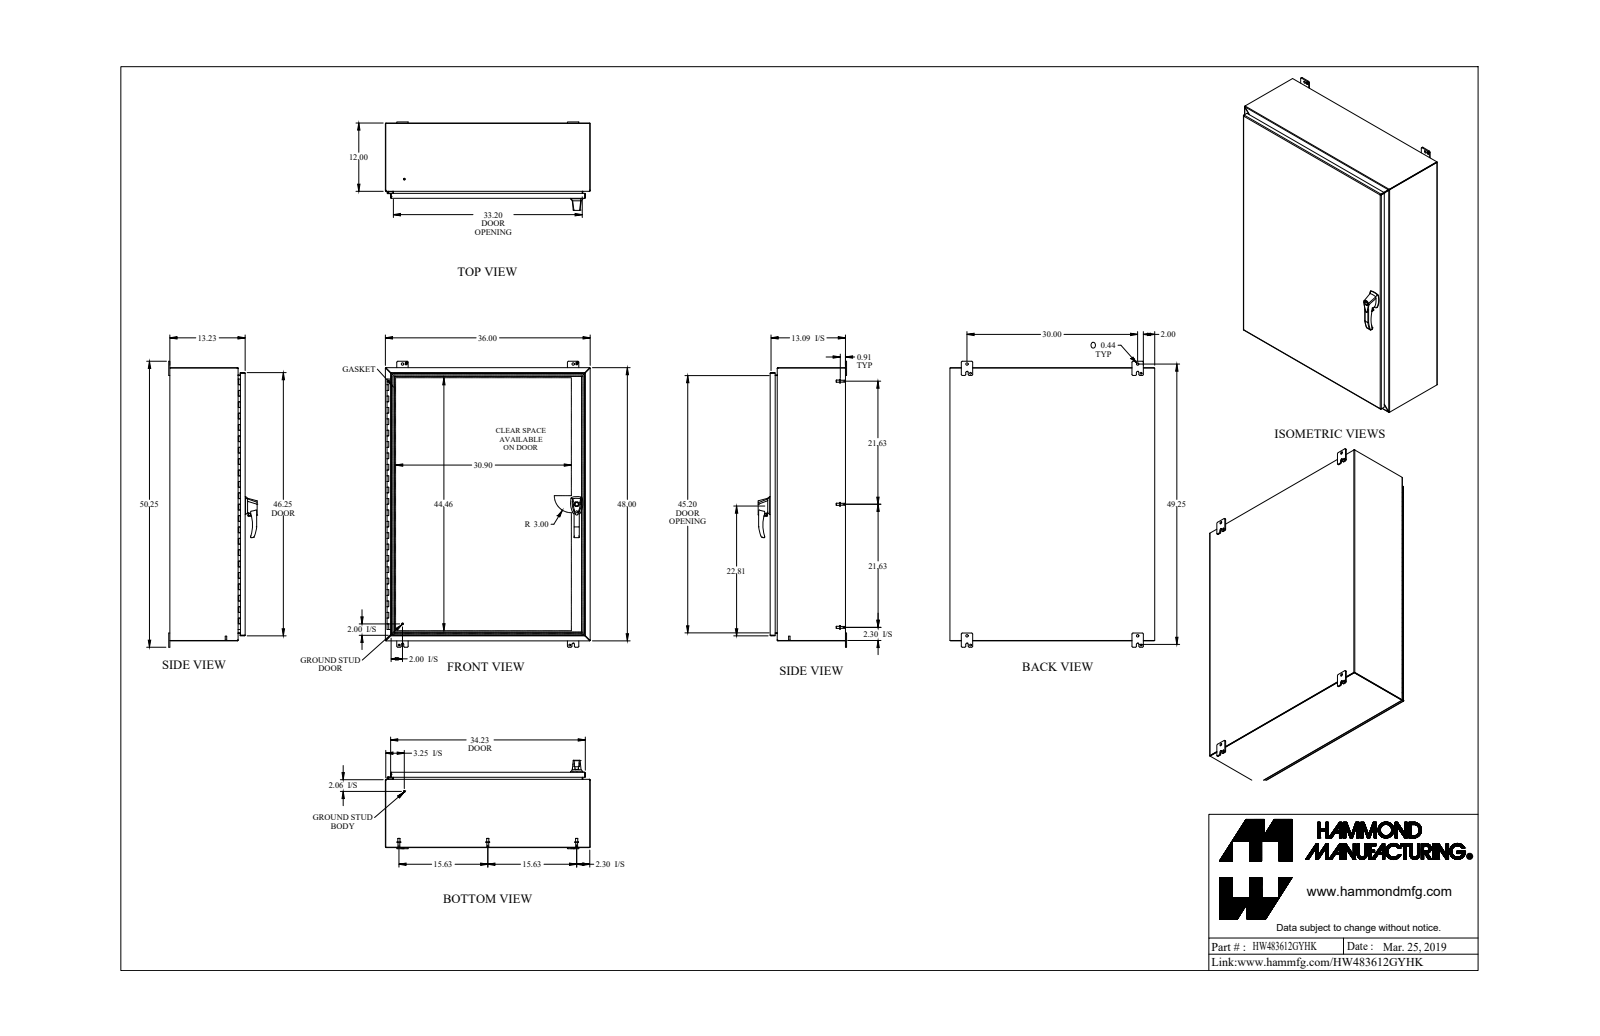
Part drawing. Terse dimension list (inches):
name: HW483612GYHK
written by: SolidWorks 2018 (AUTOMOTIVE_DESIGN)
unit: in
bodies: 49 solids, 1635 faces (754 planar, 686 cylindrical, 195 other)
size: 50.25 × 36 × 15.535
volume: 524.2 in³; area: 13 072 in²
holes: 6× ⌀0.176, 4× ⌀0.25, 4× ⌀0.313, 3× ⌀0.196, 3× ⌀0.265, 3× ⌀0.413, 2× ⌀0.256, 2× ⌀0.394, 2× ⌀0.437, 1× ⌀0.187, 1× ⌀0.233, 1× ⌀0.334
bosses: 13× ⌀0.375, 8× ⌀0.65, 8× ⌀0.33, 6× ⌀0.25, 6× ⌀0.156, 3× ⌀1, 2× ⌀0.63, 2× ⌀0.51
rounds: 24× R0.188, 14× R0.036, 14× R0.108, 12× R0.116, 12× R0.187, 11× R0.25, 9× R0.125, 8× R0.04
face distances: 0.072, 13.138, 13.066, 0.095, 13.233, 13.161, 35.928, 47.928, 35.856, 36
hole spacings: 20.118, 20.119, 40.237, 1.111, 20.119, 30, 30.661, 39.146
